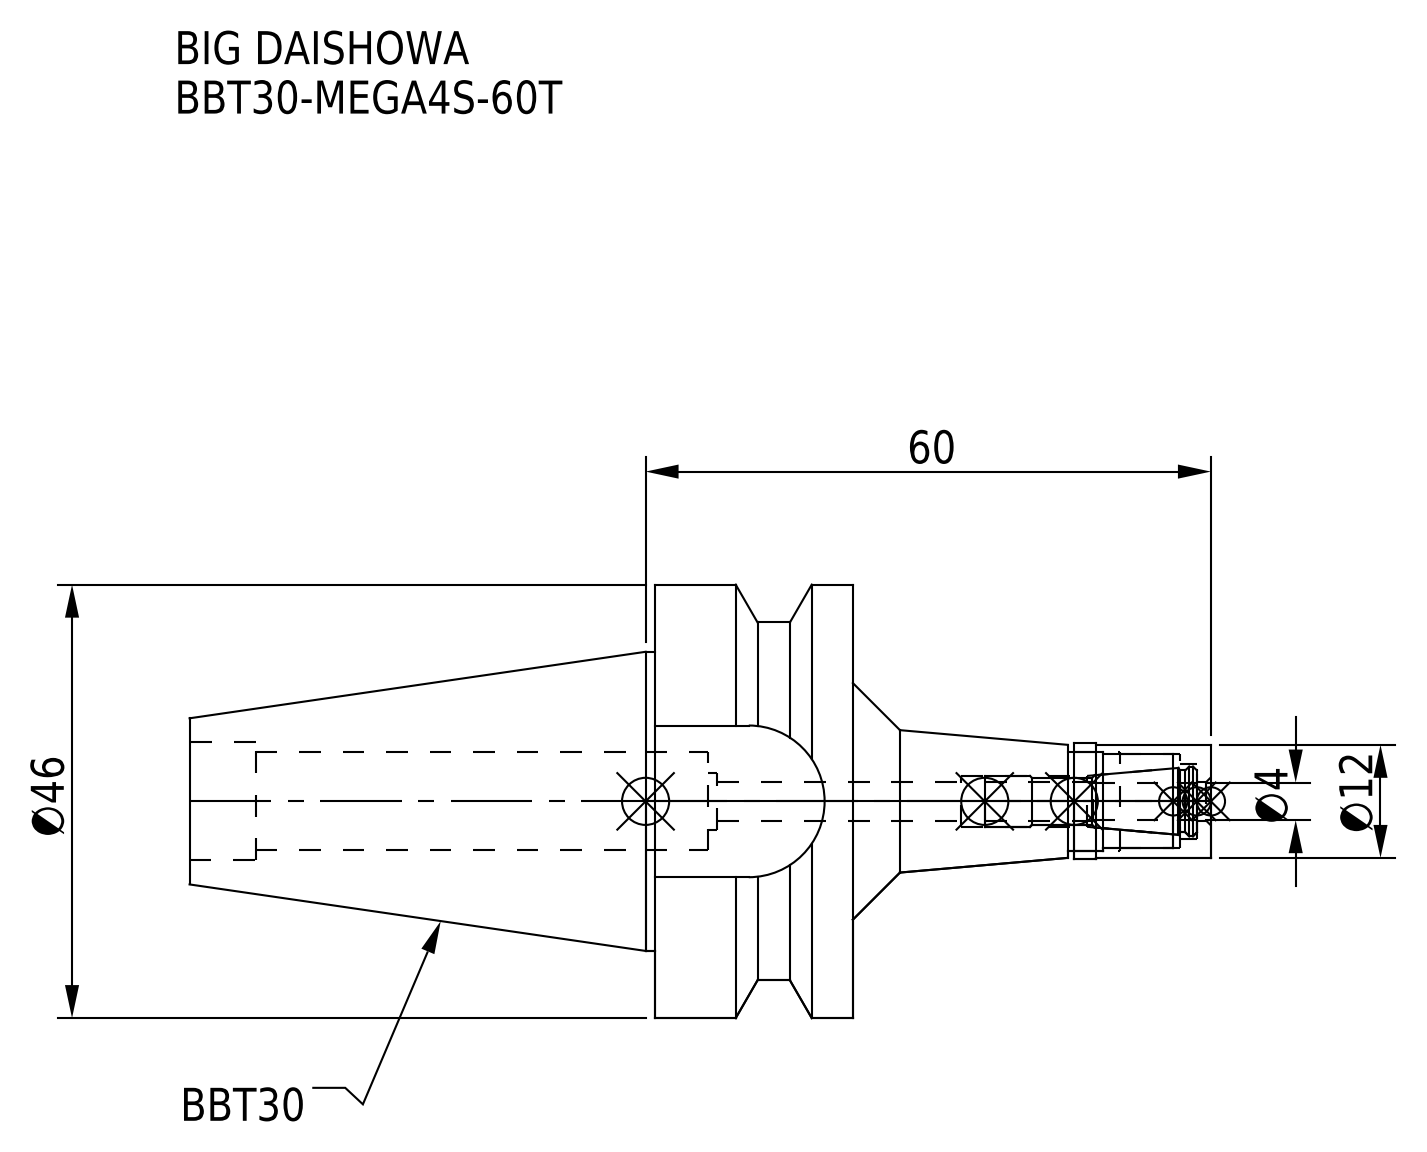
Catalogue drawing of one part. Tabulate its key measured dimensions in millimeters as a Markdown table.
| quantity | value |
| --- | --- |
| part name | BBT30-MEGA4S-60T; BBT30-MEGA4S-60T-FreeParts; BBT30-MEGA4S-60T_1.stp; BBT30-MEGA4S-60T.stp (+3 more) |
| STEP written by | SolidWorks 2019 (CONFIG_CONTROL_DESIGN) |
| units | millimeters |
| bodies | 2 solids, 74 faces (22 planar, 38 cylindrical, 14 other) |
| overall size | 108.4 × 46 × 46 |
| volume | 53 657 mm³ |
| surface area | 15 159 mm² |
| round holes (diameter × count) | 4.1 × 1, 4.2 × 1, 5.4 × 1, 6 × 1, 8 × 1, 10 × 1, 10.4 × 1, 10.5 × 1, 12.5 × 1 |
| round bosses / shafts (diameter × count) | 46 × 1, 31.75 × 1, 12.3 × 1, 12 × 1 |
| partial cylindrical surfaces (radius × count) | 8.05 × 1, 19 × 1 |
| main face-to-face distances | 21, 32.6, 49.4, 70.4, 16.1, 55, 38, 59, 108.4, 0.7 |
